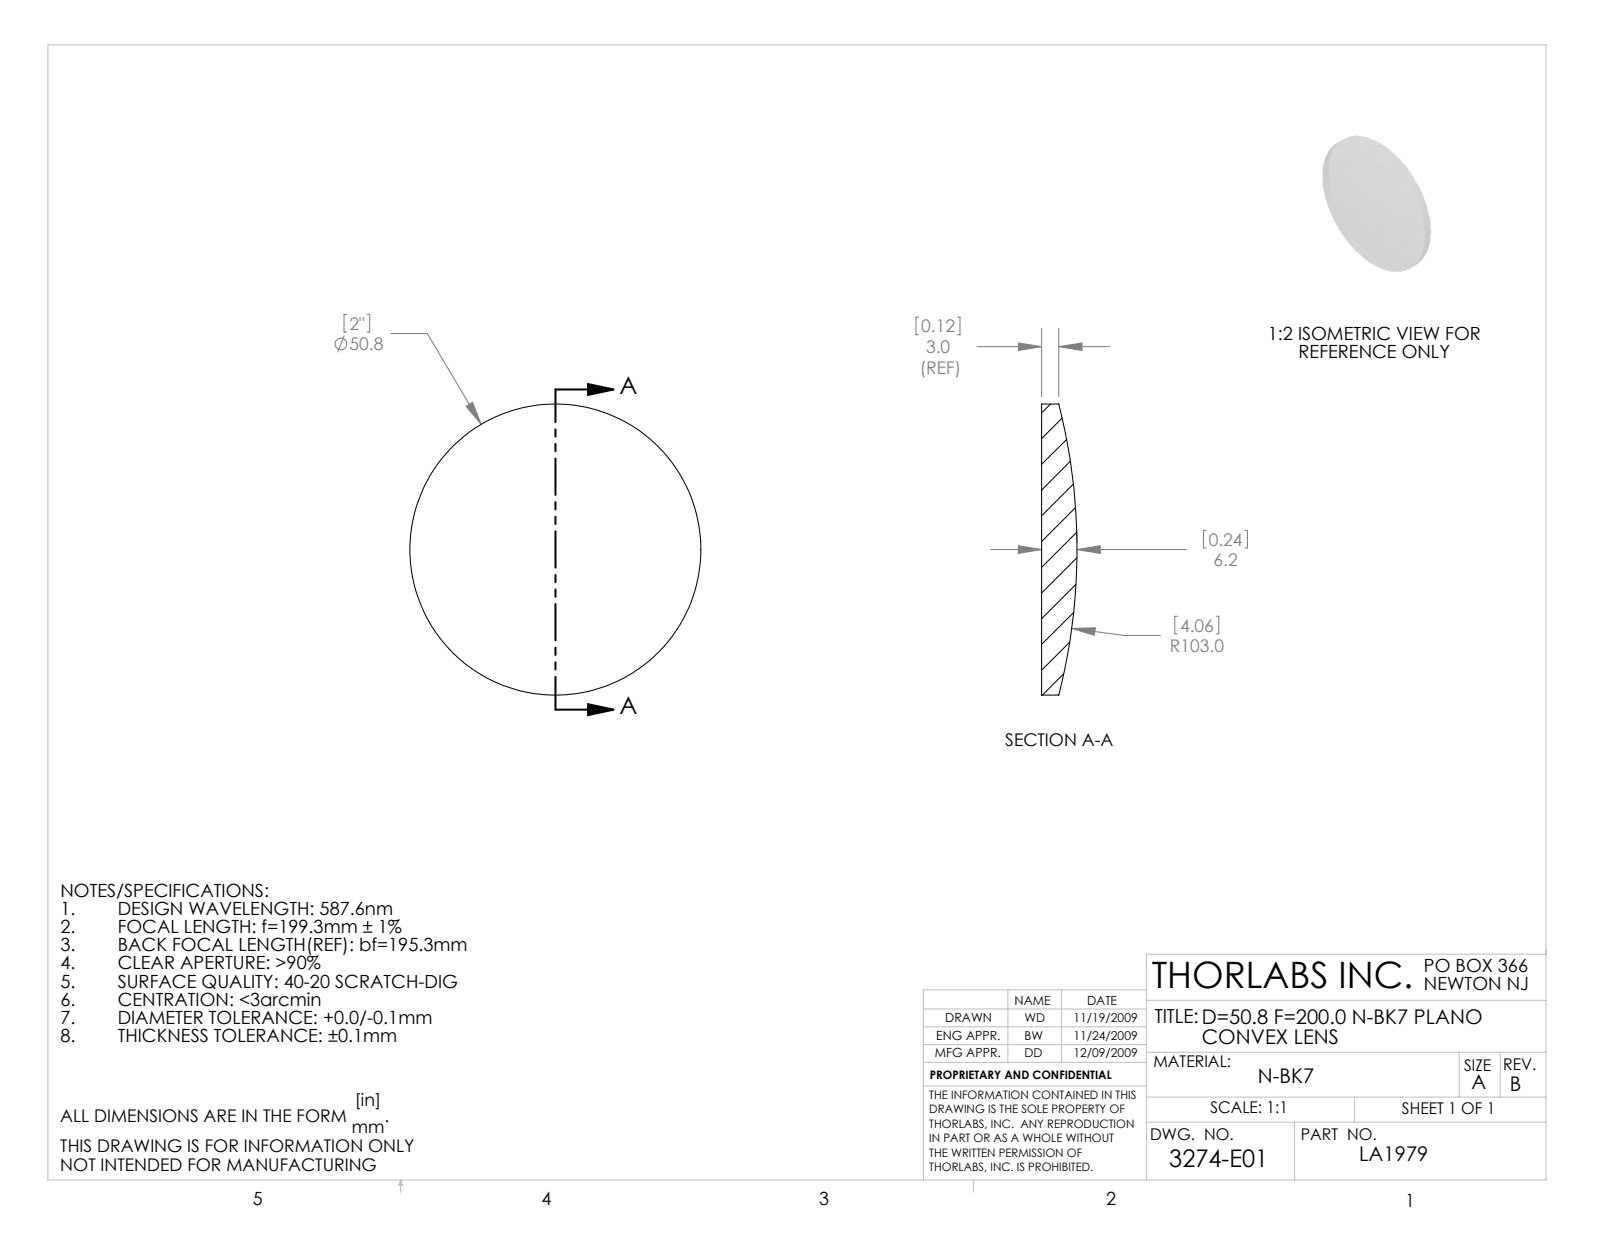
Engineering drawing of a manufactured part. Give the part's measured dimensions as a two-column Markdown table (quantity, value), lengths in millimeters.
| quantity | value |
| --- | --- |
| part name | 3274-E0W |
| STEP written by | SolidWorks 2009 (AUTOMOTIVE_DESIGN) |
| units | millimeters |
| bodies | 1 solid, 5 faces (1 planar, 2 cylindrical, 2 other) |
| overall size | 50.8 × 50.8 × 6.18 |
| volume | 9 319 mm³ |
| surface area | 4 564 mm² |
| round bosses / shafts (diameter × count) | 50.8 × 1 |
